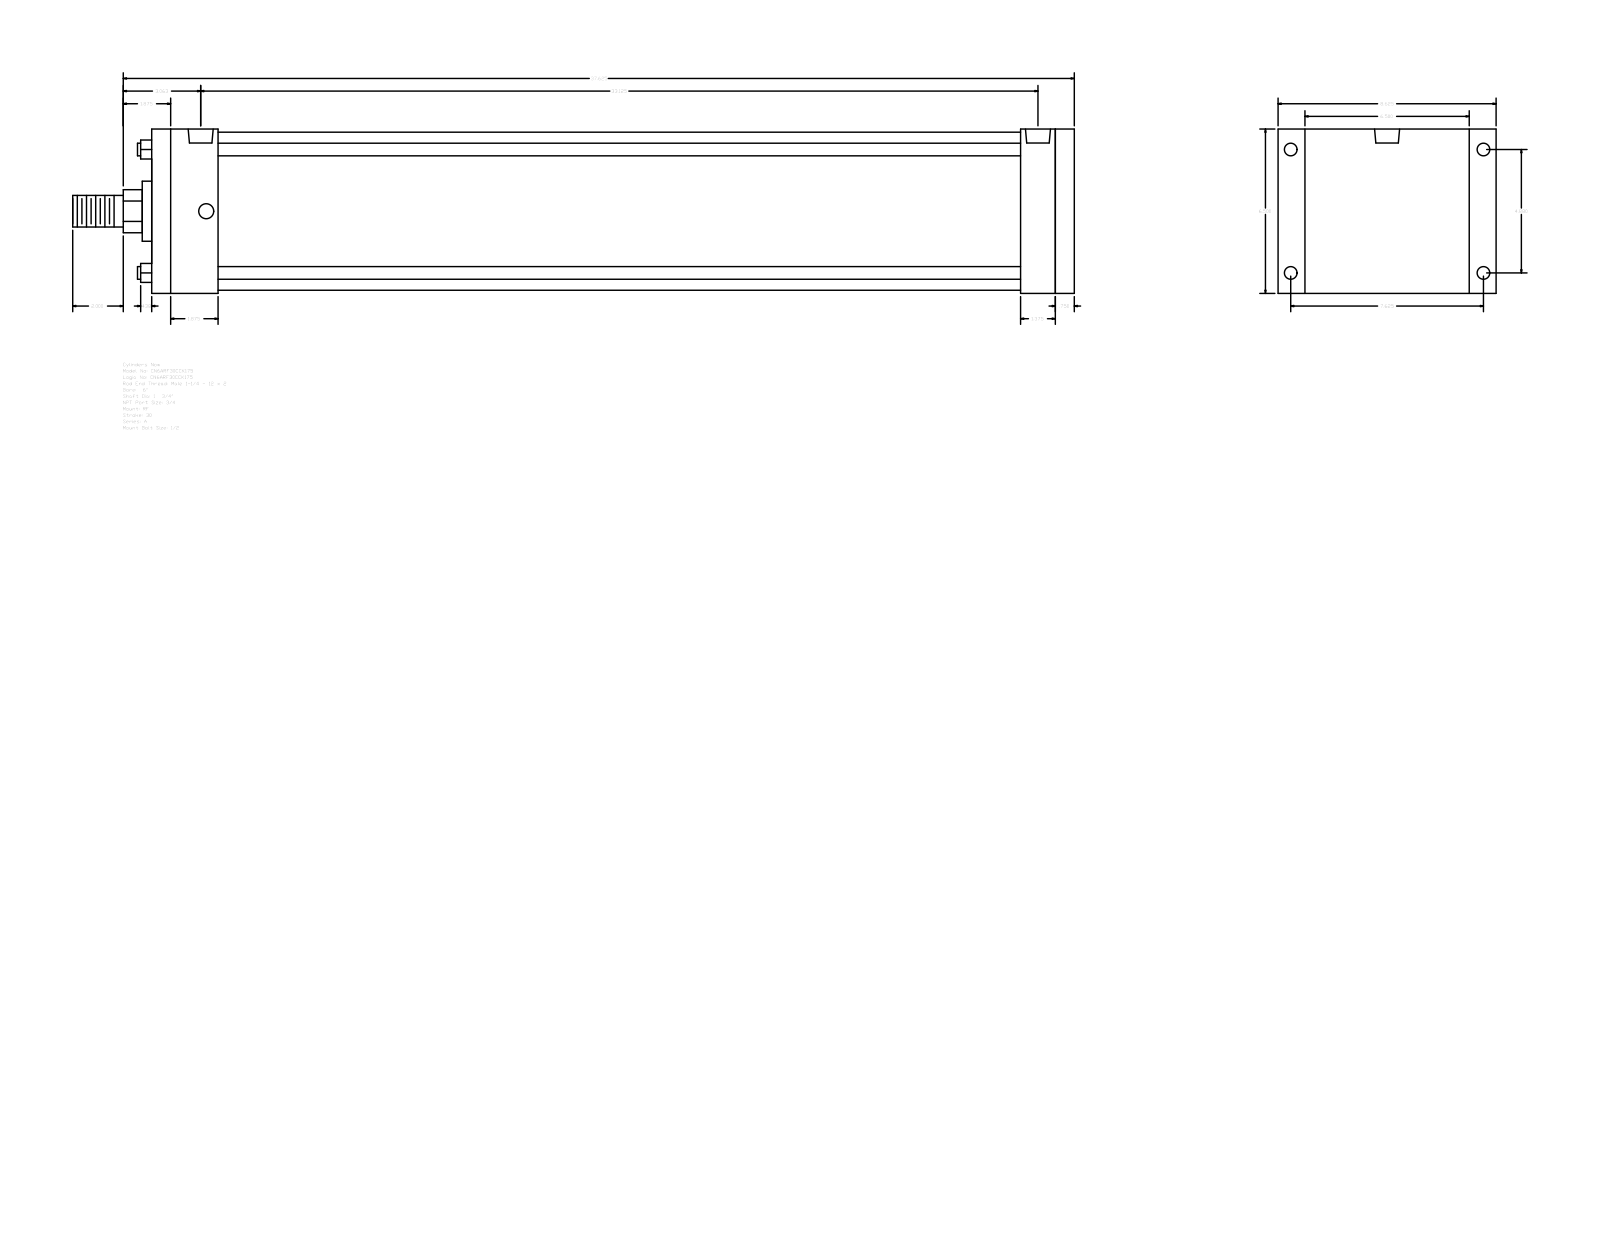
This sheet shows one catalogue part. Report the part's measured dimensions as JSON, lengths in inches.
{"part_name": "A_RF__0600_1.75", "step_written_by": "GSSL Pune (CONFIG_CONTROL_DESIGN)", "units": "inches", "bodies": {"solids": 0, "faces": 92, "planar": 64, "cylindrical": 28, "other": 0}, "overall_size": [39.625, 8.625, 6.5], "round_holes": [[0.5, 4], [0.594, 4], [0.989, 2]], "round_bosses_or_shafts": [[0.5, 4], [6.25, 1], [2.375, 1], [1.75, 1], [1.25, 1]], "partial_cylinders_radius": [[0.852, 1]], "face_to_face_distances": [6.5, 36.5, 0.75, 35.75, 2.625, 33.125, 33.875, 34.375, 31.75, 1.375], "hole_center_spacings": [0.219, 4.88, 7.625, 9.053, 32.687, 32.906, 33.125]}
